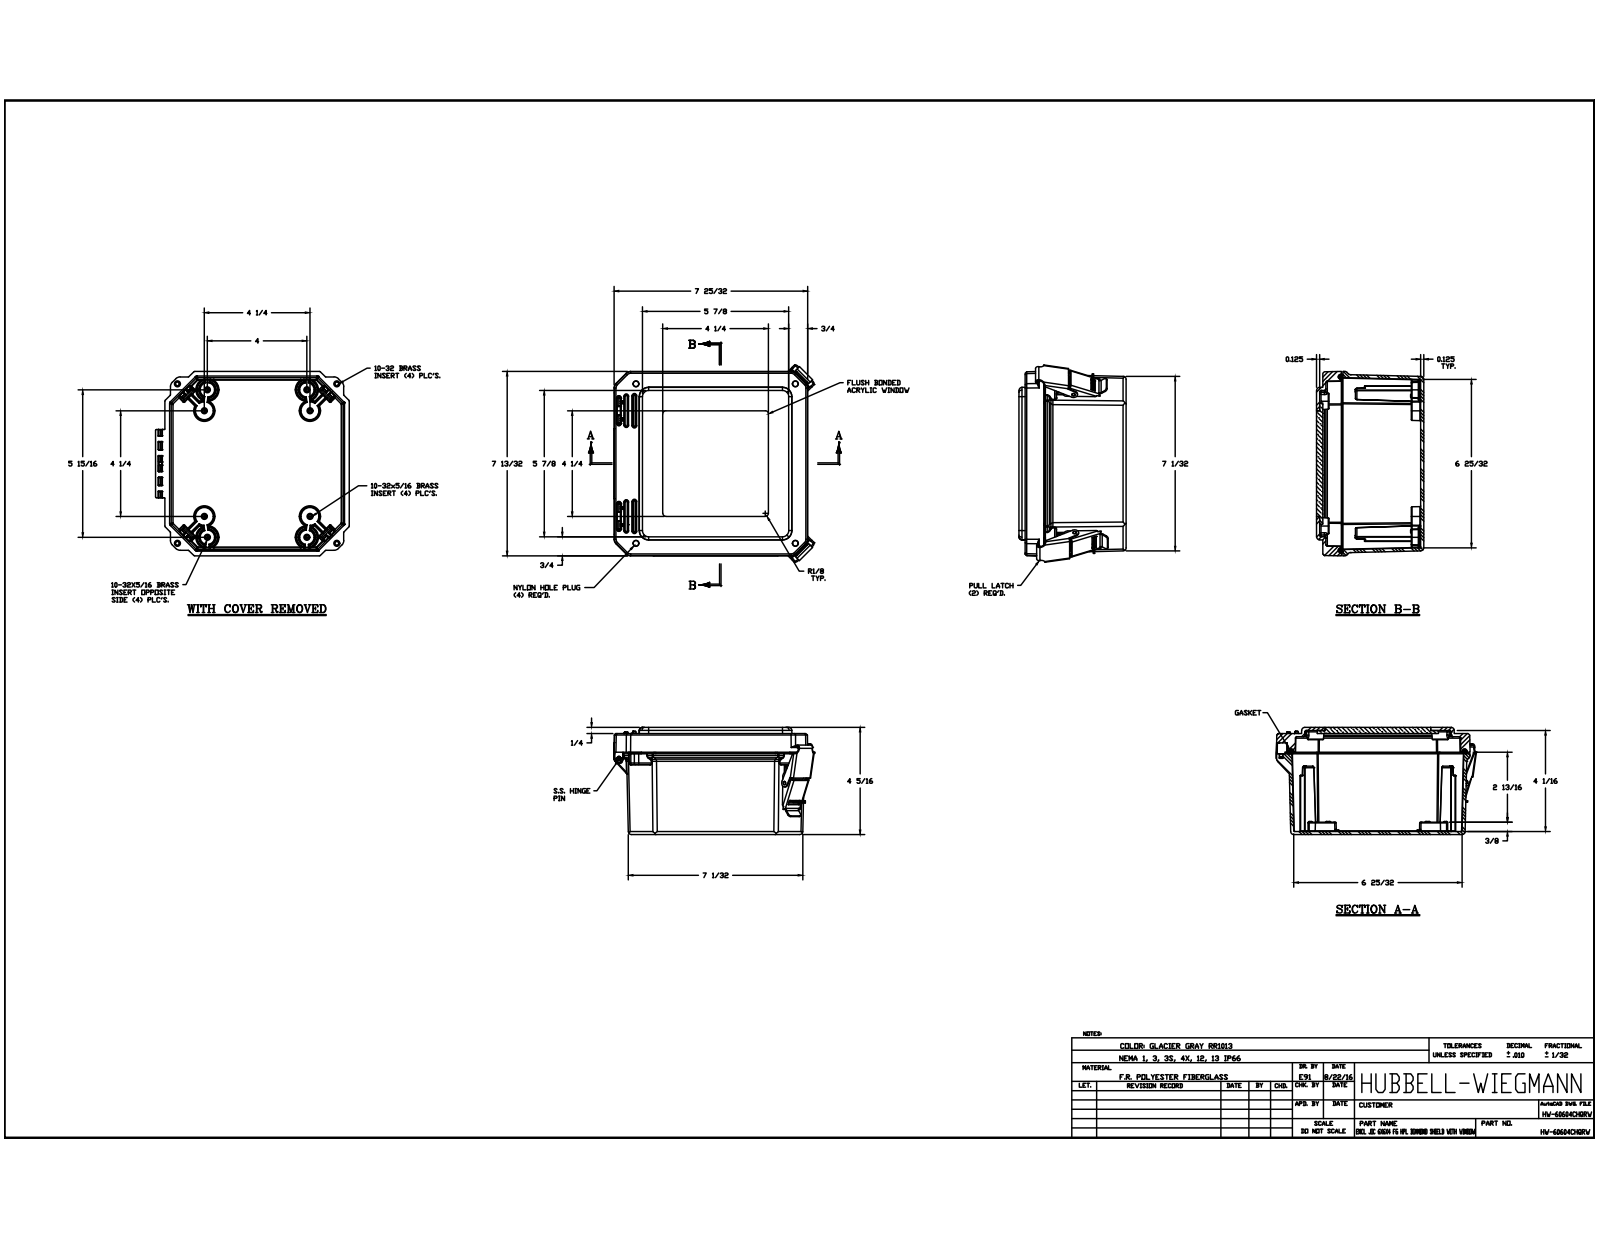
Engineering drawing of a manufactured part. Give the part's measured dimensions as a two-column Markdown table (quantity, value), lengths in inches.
| quantity | value |
| --- | --- |
| part name | DSW60604HPL_STP; DS060604BOX; BRASS INSERT-(; BRASS INSERT-(_1 (+8 more) |
| STEP written by | Autodesk Inventor 2017 (AUTOMOTIVE_DESIGN) |
| units | inches |
| bodies | 34 solids, 2150 faces (753 planar, 851 cylindrical, 546 other) |
| overall size | 8.107 × 8.044 × 4.312 |
| volume | 40.59 in³ |
| surface area | 544.5 in² |
| round holes (diameter × count) | 0.156 × 16, 0.152 × 8, 0.135 × 6, 0.15 × 4, 0.252 × 4, 0.253 × 4, 0.135 × 2, 0.219 × 2, 0.227 × 2, 0.313 × 2, 0.375 × 2, 0.137 × 1 |
| round bosses / shafts (diameter × count) | 0.246 × 16, 0.87 × 4, 0.209 × 4, 0.435 × 2, 0.3 × 2, 0.135 × 1 |
| partial cylindrical surfaces (radius × count) | 0.01 × 109, 0.005 × 80, 0.02 × 63, 0.03 × 63, 0.06 × 34, 0.063 × 28, 0.09 × 26, 0.125 × 26 |
| main face-to-face distances | 0.125, 0.125, 4.06, 0.25, 0.124, 4.087, 3.962, 0.252, 4.312, 4.187 |
| hole center spacings | 7.541, 4.25, 5.441, 5.441, 1.53, 5.759, 8.075, 6.01 |
